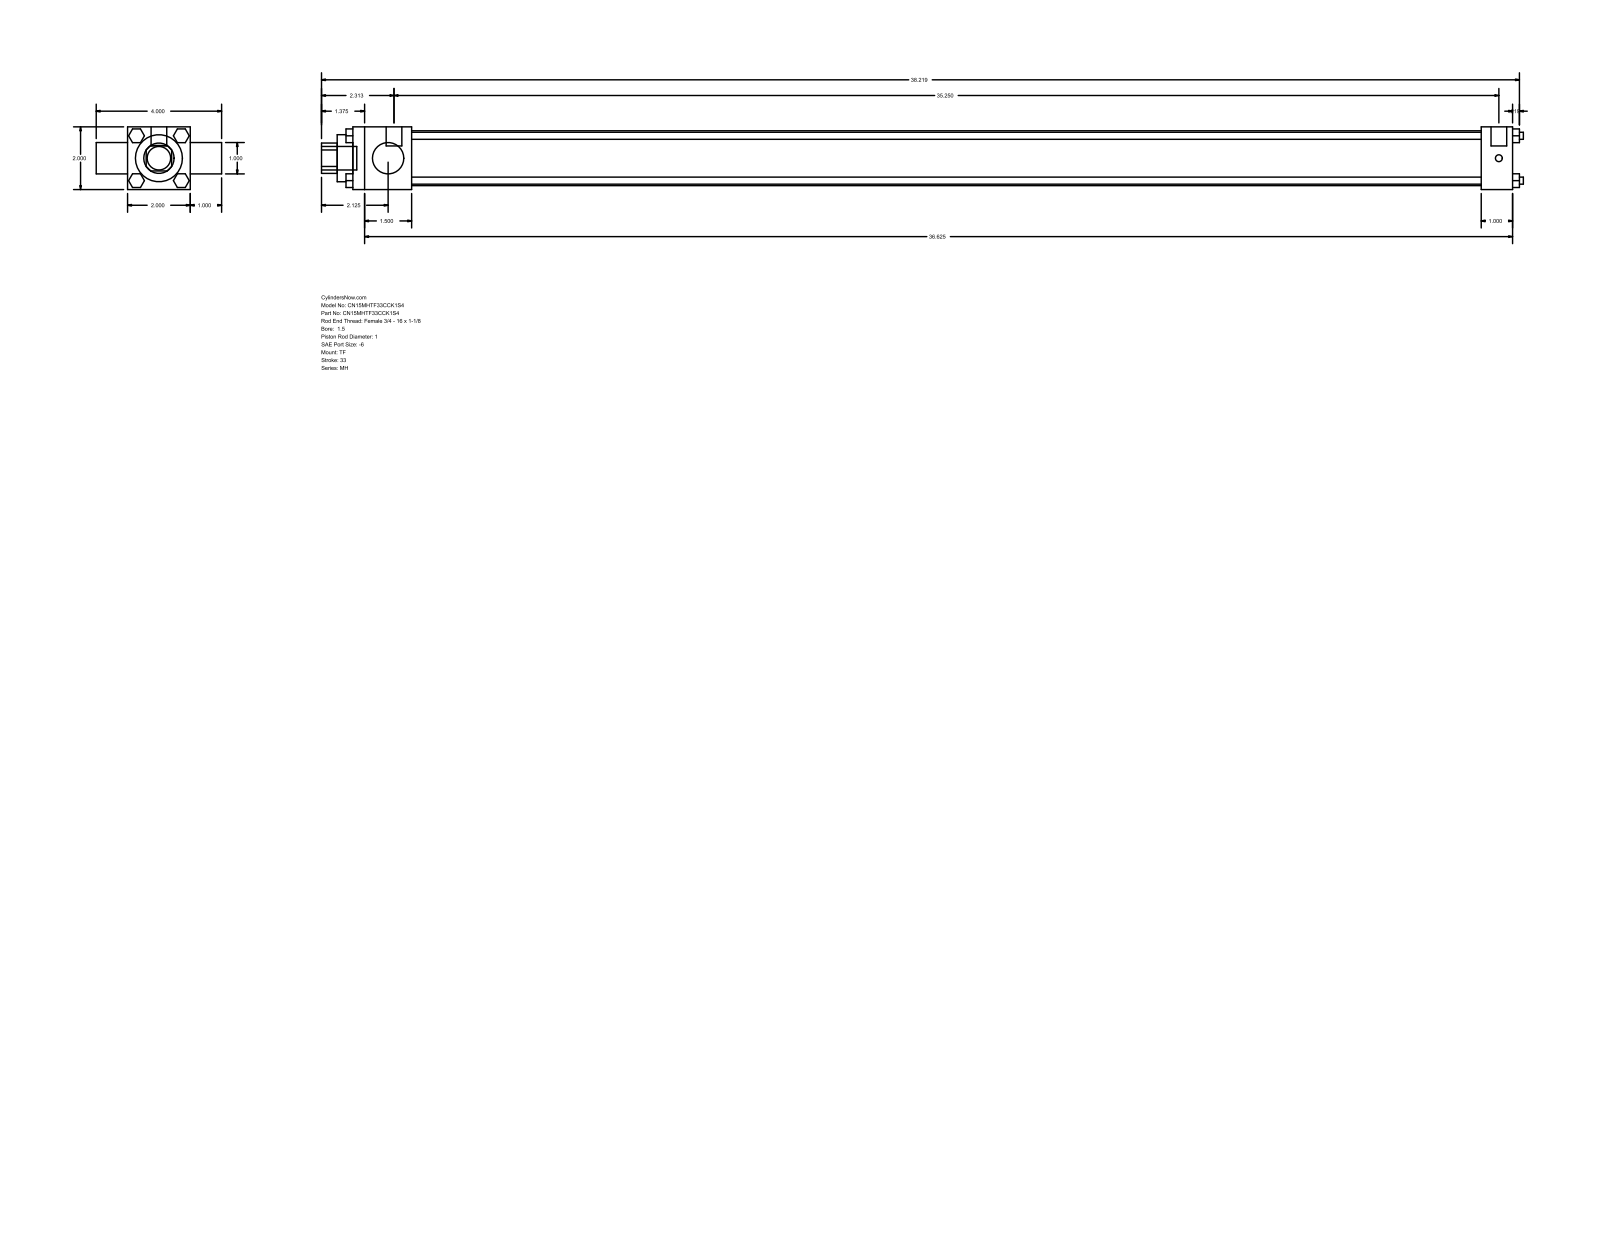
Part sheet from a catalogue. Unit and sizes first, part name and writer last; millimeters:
Units: millimetres
Overall size (bounding box): 973.93 × 101.6 × 50.8
Round holes (diameter × count): ⌀25.4 ×2, ⌀38.1 ×1, ⌀44.45 ×1
Round bosses / shafts (diameter × count): ⌀5.71 ×4, ⌀5.56 ×3, ⌀12.7 ×2, ⌀19.05 ×1
Partial cylindrical surfaces — rounded edges, fillets, slot ends (radius × count): R12.29 ×1
Main face-to-face distances: 50.8, 25.4, 939.8, 76.2, 47.63, 892.17, 914.4, 866.77, 945.36, 12.7
Bodies: 0 solids, 120 faces (92 planar, 28 cylindrical, 0 other)
Part name (STEP PRODUCT): MH_TF__0150_1
STEP written by: GSSL Pune (CONFIG_CONTROL_DESIGN)
